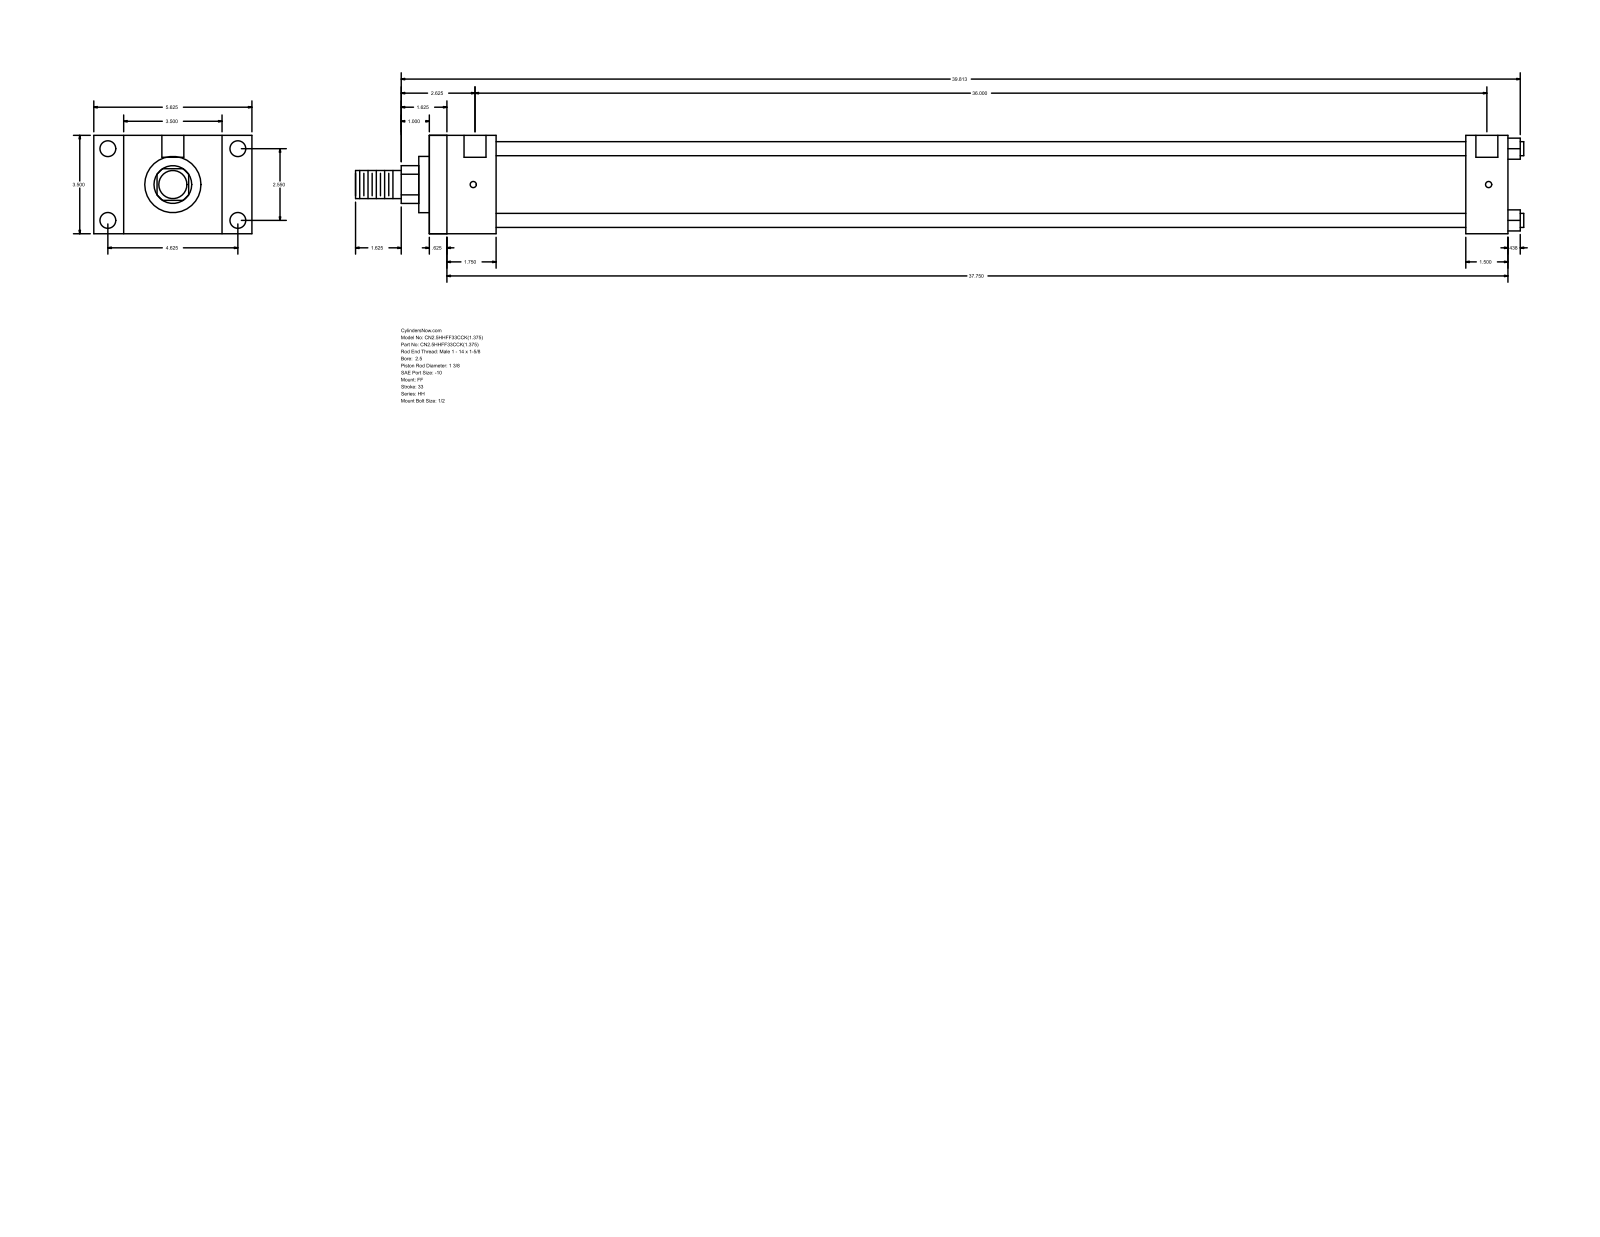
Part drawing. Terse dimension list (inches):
name: HH_FF__0250_1.375
written by: GSSL Pune (CONFIG_CONTROL_DESIGN)
unit: in
bodies: 0 solids, 92 faces (64 planar, 28 cylindrical, 0 other)
size: 41.563 × 5.625 × 3.5
holes: 4× ⌀0.219, 4× ⌀0.563, 2× ⌀0.781
bosses: 4× ⌀0.5, 1× ⌀2.875, 1× ⌀2, 1× ⌀1.375, 1× ⌀1
rounds: 1× R0.672
face distances: 3.5, 38.375, 0.625, 37.75, 2.375, 1.75, 36, 36.875, 36.25, 34.5
hole spacings: 0.062, 2.55, 4.625, 5.281, 36.063, 36.125, 36
